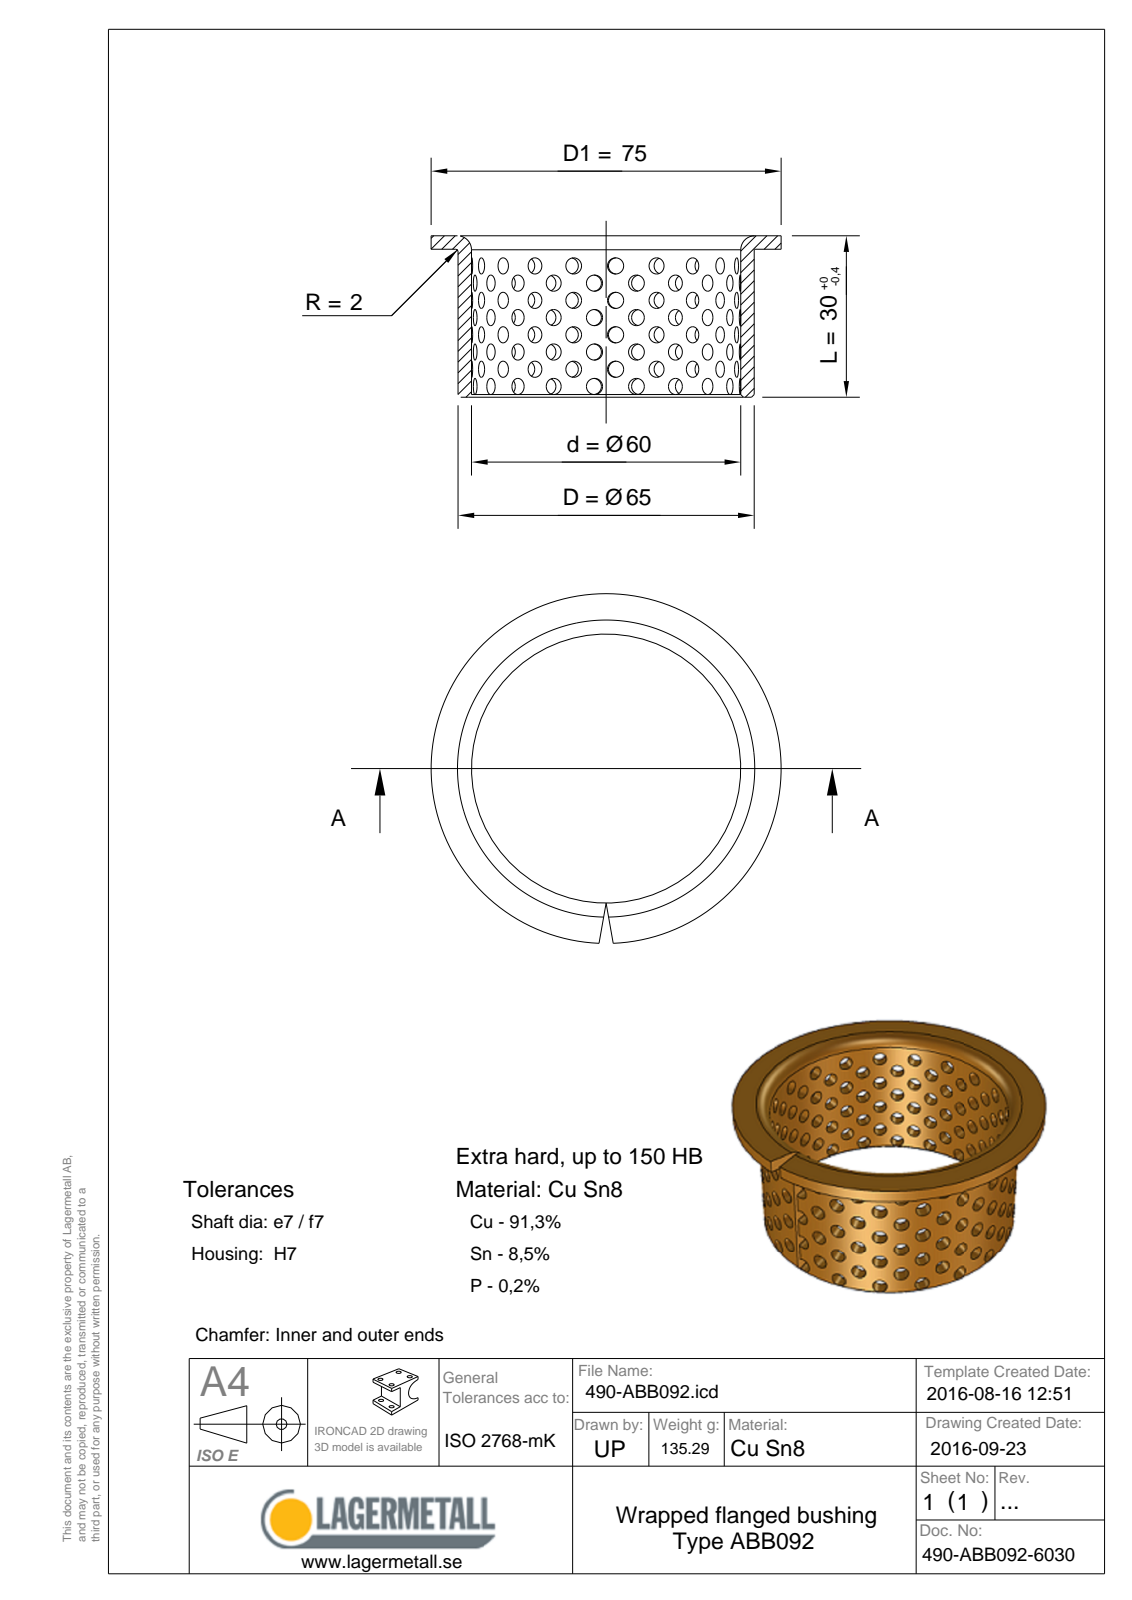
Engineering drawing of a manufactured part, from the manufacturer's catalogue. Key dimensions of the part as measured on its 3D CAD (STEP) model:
STEP written by: Spatial InterOp 3D (CONFIG_CONTROL_DESIGN)
Units: millimetres
Bodies: 1 solid, 25 faces (5 planar, 8 cylindrical, 12 other)
Overall size (bounding box): 75 × 75 × 30
Volume: 16 703 mm³ · Surface area: 14 516 mm²
Round holes (diameter × count): ⌀60 ×1
Round bosses / shafts (diameter × count): ⌀75 ×1, ⌀65 ×1
Main face-to-face distances: 2.5, 27.5, 30
